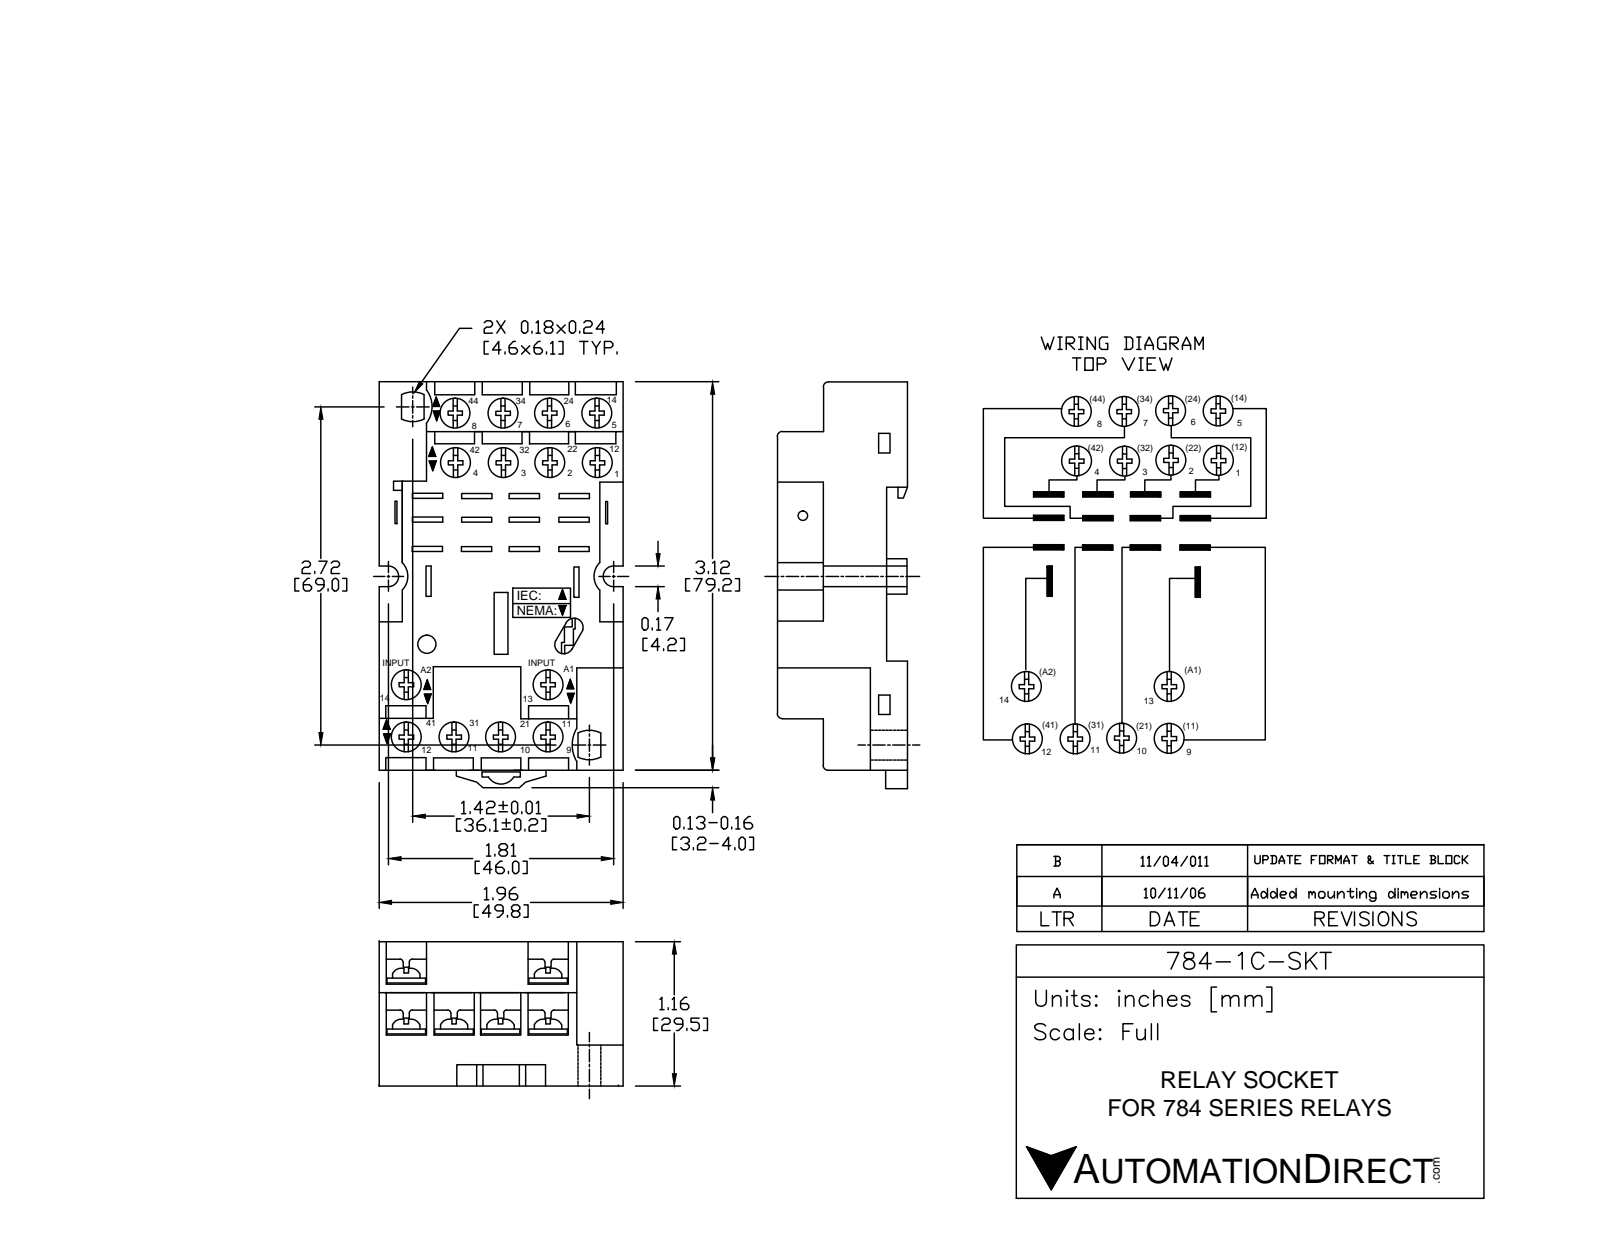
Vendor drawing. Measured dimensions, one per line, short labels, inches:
name: 784-4C-SKT-1
written by: SolidWorks 2021 (CONFIG_CONTROL_DESIGN)
unit: in
bodies: 1 solid, 360 faces (308 planar, 52 cylindrical, 0 other)
size: 3.33 × 1.96 × 1.18
volume: 5.366 in³; area: 29.98 in²
holes: 14× ⌀0.24, 1× ⌀0.16
rounds: 8× R0.02, 6× R0.08, 3× R0.14, 2× R0.06
face distances: 1.18, 1.96, 1.02, 0.16, 0.44, 0.1, 0.74, 0.04, 0.73, 1.57
hole spacings: 0.382, 0.764, 0.36, 0.525, 0.845, 1.146, 2.372, 2.728
